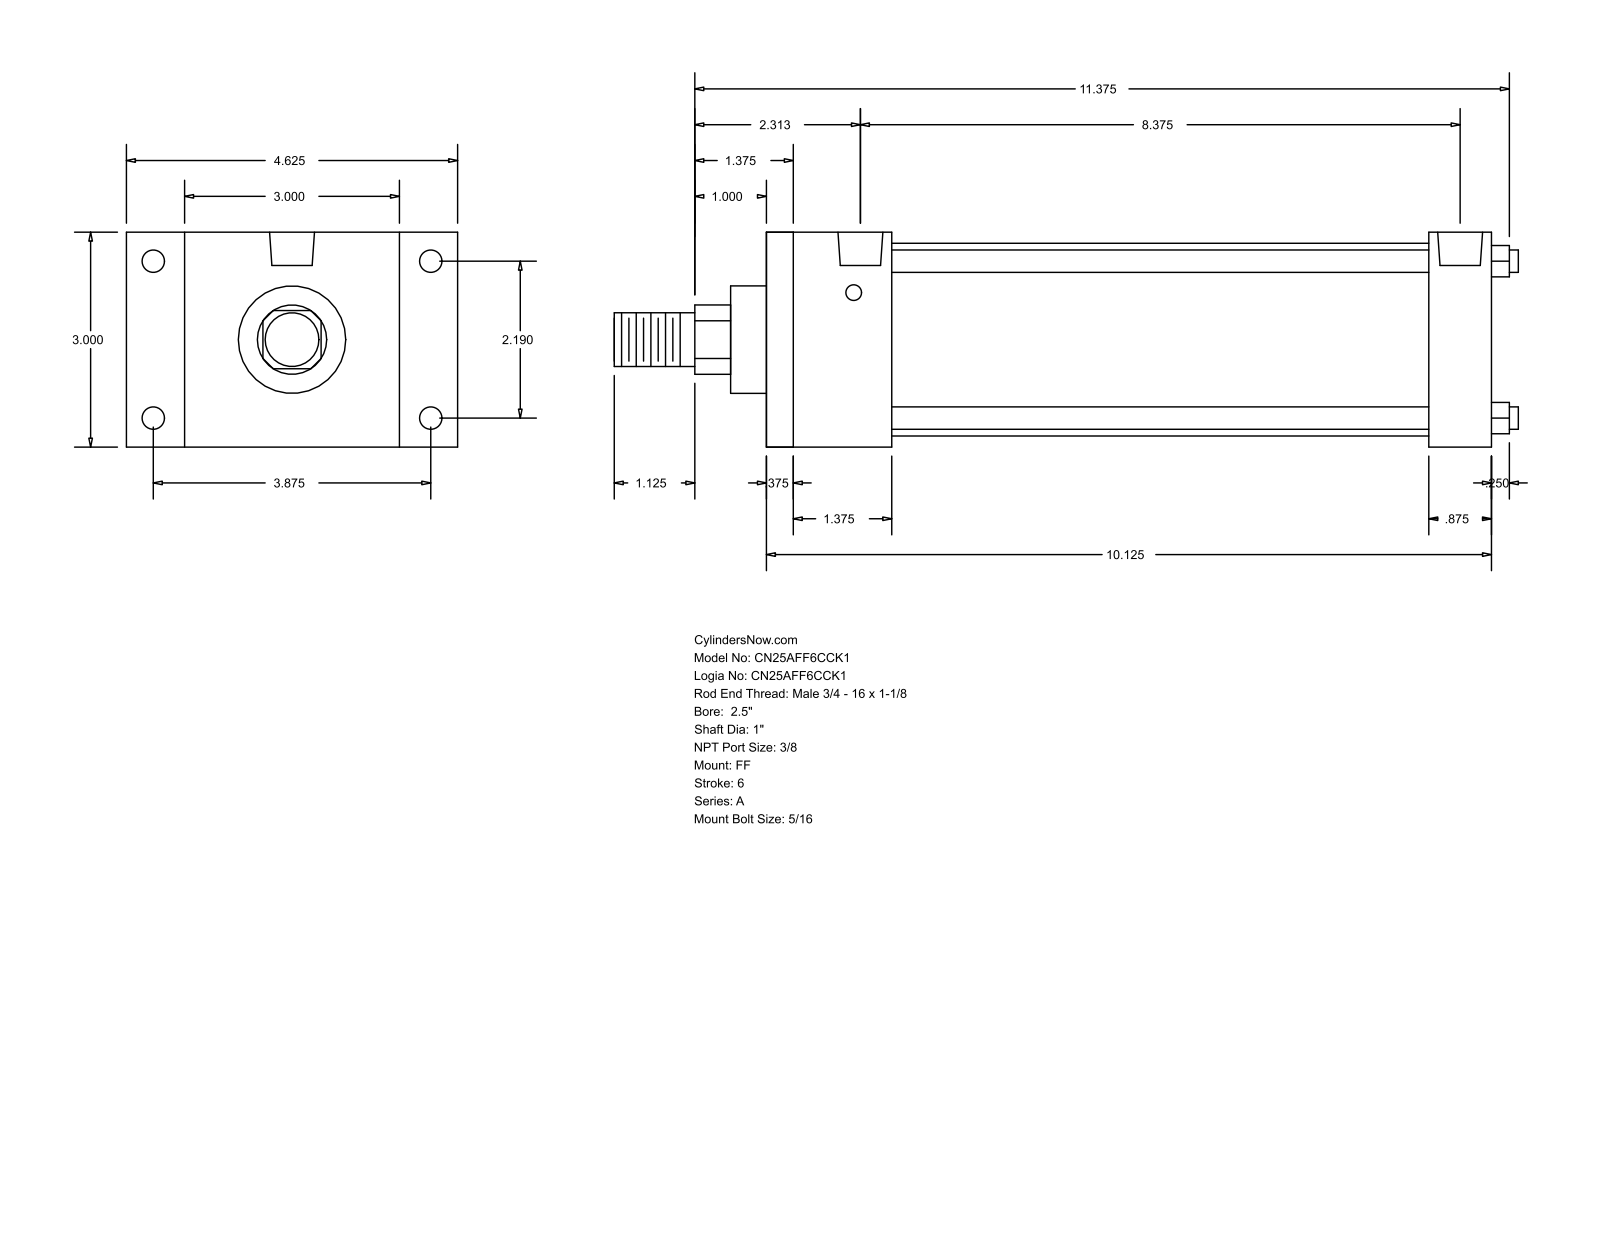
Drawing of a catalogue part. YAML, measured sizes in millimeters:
part_name: "A_FF__0250_1"
step_written_by: "GSSL Pune (CONFIG_CONTROL_DESIGN)"
units: millimeters
bodies: {solids: 0, faces: 92, planar: 64, cylindrical: 28, other: 0}
overall_size: [320.68, 117.47, 76.2]
round_holes:
  - {diameter: 5.56, count: 4}
  - {diameter: 7.94, count: 4}
  - {diameter: 15.93, count: 2}
round_bosses_or_shafts:
  - {diameter: 7.94, count: 4}
  - {diameter: 68.33, count: 1}
  - {diameter: 38.1, count: 1}
  - {diameter: 25.4, count: 1}
  - {diameter: 19.05, count: 1}
partial_cylinders:
  - {radius: 12.29, count: 1}
face_to_face_distances: [76.2, 257.17, 247.65, 9.52, 22.22, 44.45, 234.95, 34.93, 225.43, 190.5]
hole_center_spacings: [2.38, 55.62, 98.42, 113.05, 215.1, 217.48, 212.72]
